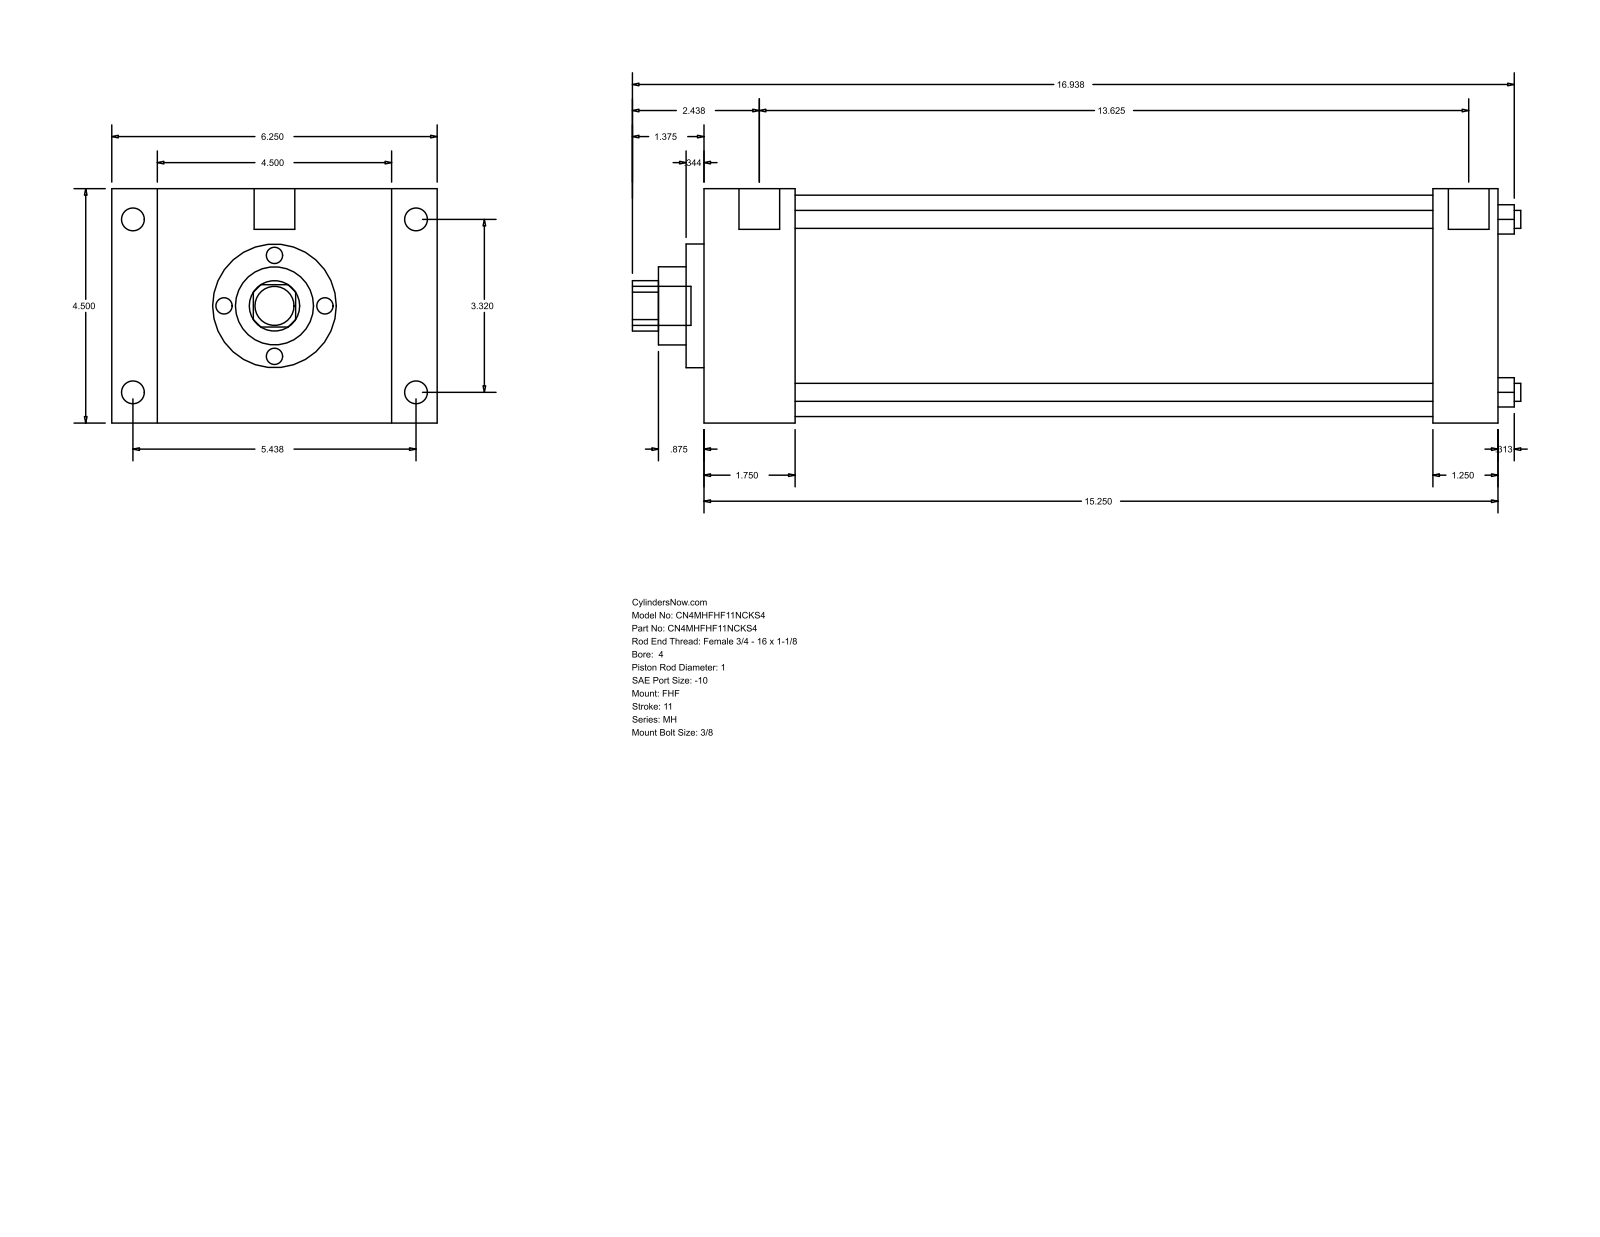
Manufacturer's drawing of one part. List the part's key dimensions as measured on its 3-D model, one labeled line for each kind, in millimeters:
Part name (STEP PRODUCT): MH_FHF__0400_1
STEP written by: GSSL Pune (CONFIG_CONTROL_DESIGN)
Units: millimetres
Bodies: 0 solids, 90 faces (61 planar, 29 cylindrical, 0 other)
Overall size (bounding box): 433.39 × 158.75 × 114.3
Round holes (diameter × count): ⌀8.76 ×4, ⌀25.4 ×1, ⌀38.1 ×1, ⌀60.33 ×1, ⌀107.95 ×1
Round bosses / shafts (diameter × count): ⌀11.13 ×4, ⌀8.73 ×4, ⌀19.84 ×2, ⌀19.05 ×1
Partial cylindrical surfaces — rounded edges, fillets, slot ends (radius × count): R12.29 ×1
Main face-to-face distances: 114.3, 387.35, 44.46, 342.89, 22.23, 136.53, 158.76, 355.6, 311.14, 31.75
Hole centre spacings: 59.62, 84.32, 119.25
